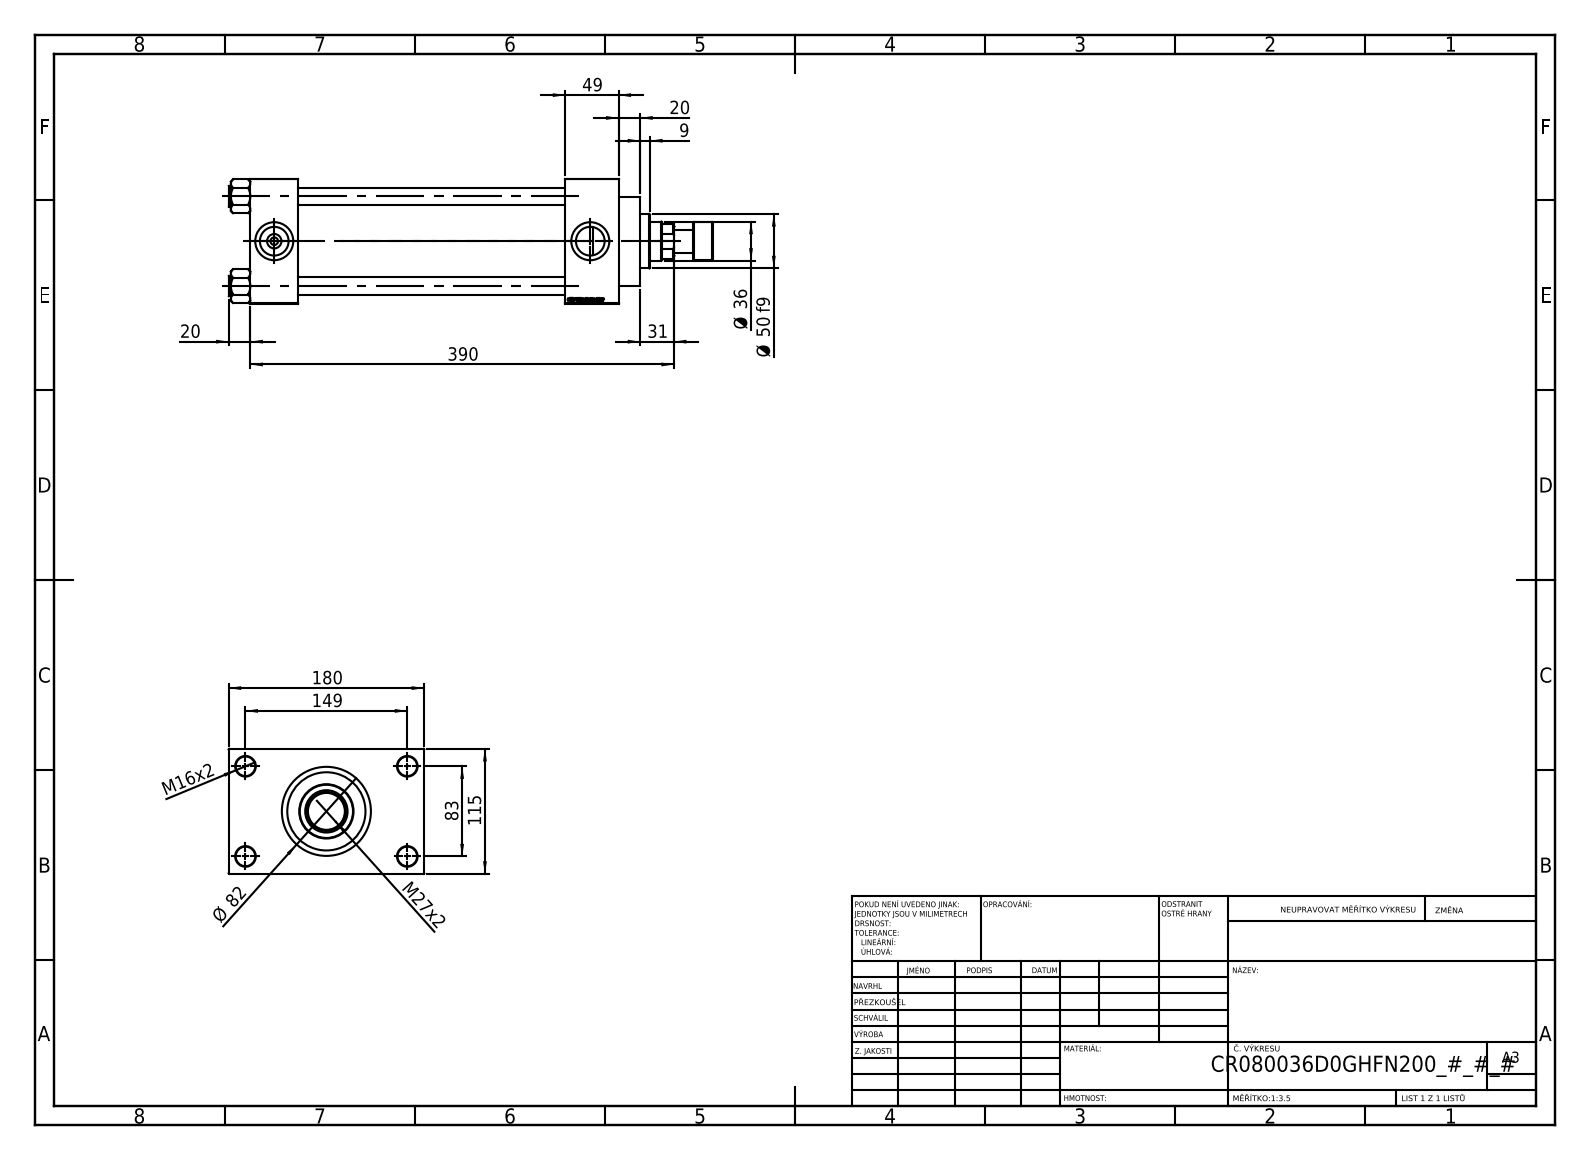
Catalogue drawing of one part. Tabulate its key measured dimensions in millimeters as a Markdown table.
| quantity | value |
| --- | --- |
| part name | V215CR_D_Body; NUT_M5_D; V215_VC_A; V215CR_ROD_END_F (+2 more) |
| STEP written by | SolidWorks 2019 (CONFIG_CONTROL_DESIGN) |
| units | millimeters |
| bodies | 12 solids, 1165 faces (549 planar, 92 cylindrical, 524 other) |
| overall size | 446 × 180 × 115 |
| volume | 2 472 000 mm³ |
| surface area | 452 581 mm² |
| round holes (diameter × count) | 16 × 4, 18 × 4, 7 × 2, 26.44 × 2, 35 × 2, 25.5 × 1, 36 × 1, 39 × 1, 61 × 1, 72 × 1, 80 × 1 |
| round bosses / shafts (diameter × count) | 19 × 4, 86 × 1, 82 × 1, 50 × 1, 35 × 1, 21 × 1 |
| main face-to-face distances | 115, 246, 49, 295, 44, 290, 339, 32.5, 147.5, 180 |
| hole center spacings | 33.15, 58.48, 82.7, 85.28, 89.24, 115.85, 142.43, 83 |
